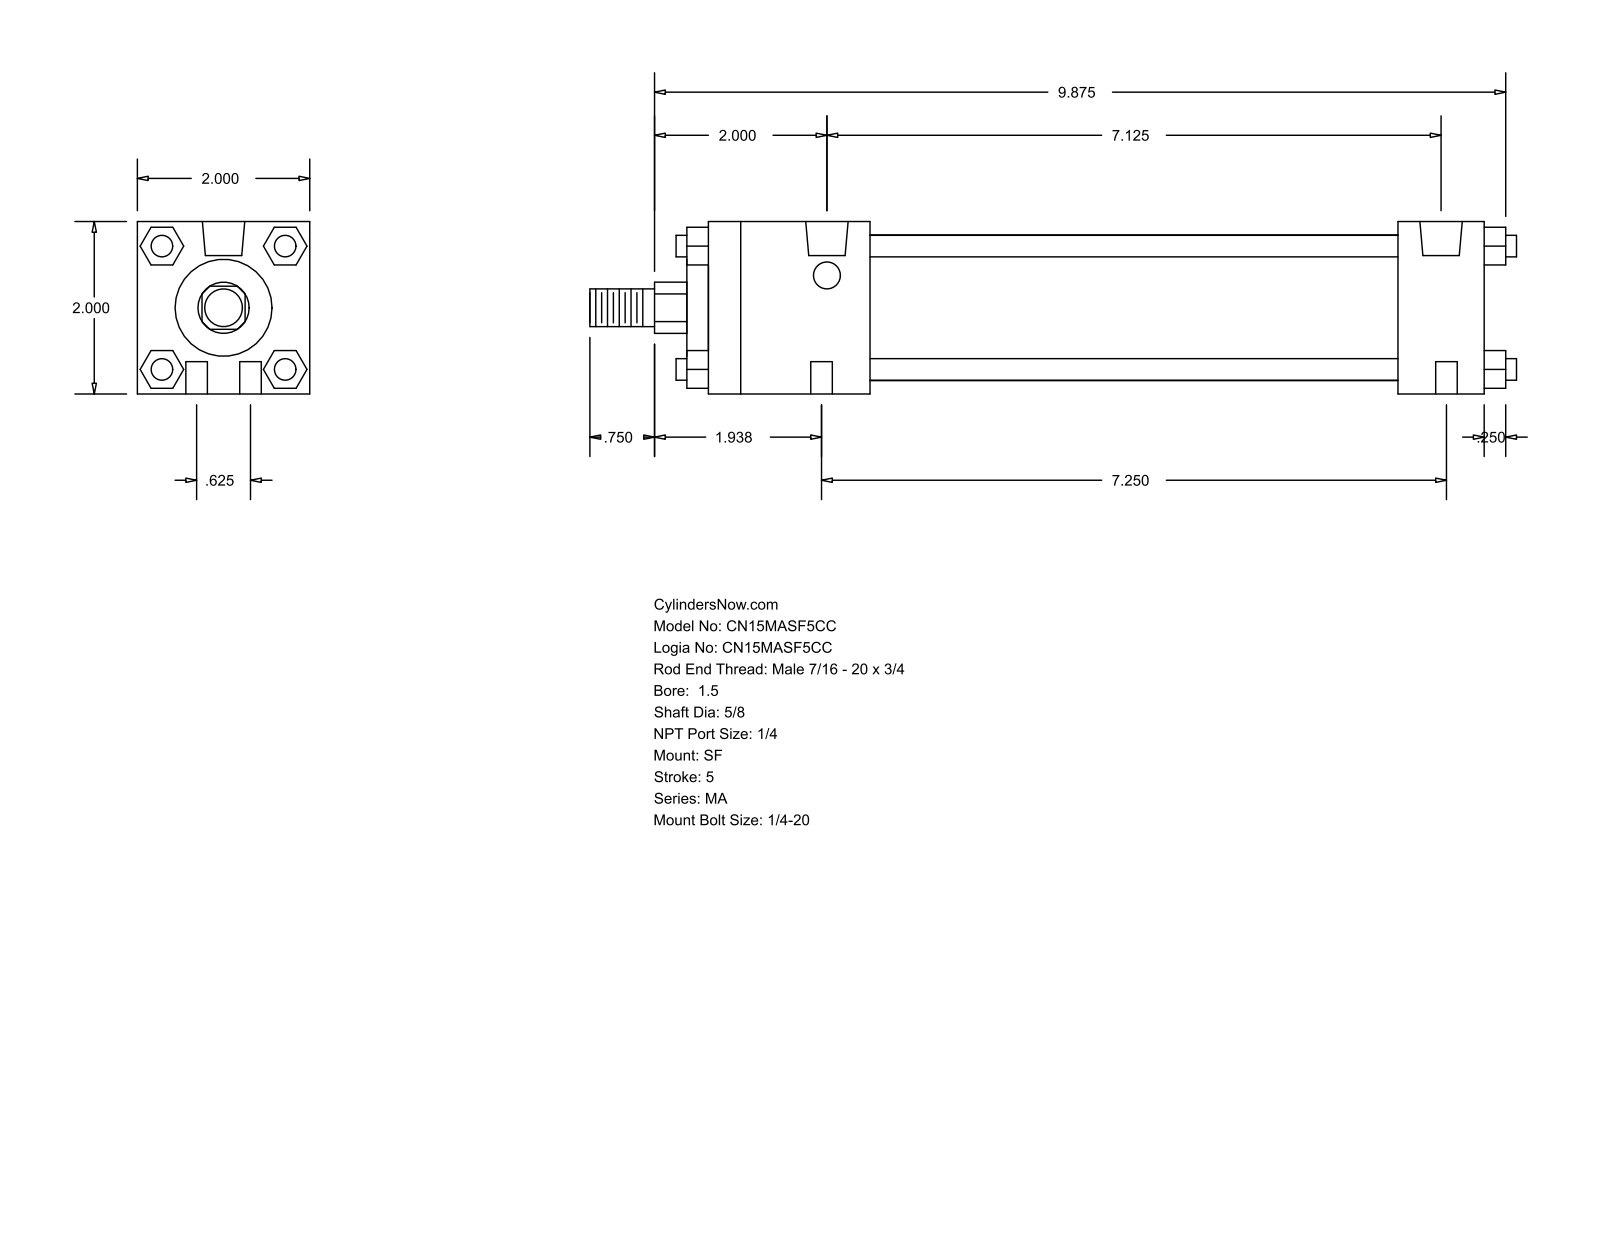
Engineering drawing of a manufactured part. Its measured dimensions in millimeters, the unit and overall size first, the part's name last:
Units: millimetres
Overall size (bounding box): 273.05 × 50.8 × 50.8
Round holes (diameter × count): ⌀6.35 ×4, ⌀7.94 ×2, ⌀12.49 ×2
Round bosses / shafts (diameter × count): ⌀6.35 ×4, ⌀42.93 ×1, ⌀28.57 ×1, ⌀15.88 ×1, ⌀11.11 ×1
Partial cylindrical surfaces — rounded edges, fillets, slot ends (radius × count): R7.54 ×1
Main face-to-face distances: 50.8, 228.59, 6.35, 25.4, 234.94, 47.62, 203.19, 155.57, 180.97, 53.97
Hole centre spacings: 8.1, 15.88, 180.98, 182.73, 182.74, 184.15, 184.83
Bodies: 0 solids, 124 faces (94 planar, 30 cylindrical, 0 other)
Part name (STEP PRODUCT): MA_SF__0150_0.625
STEP written by: GSSL Pune (CONFIG_CONTROL_DESIGN)
